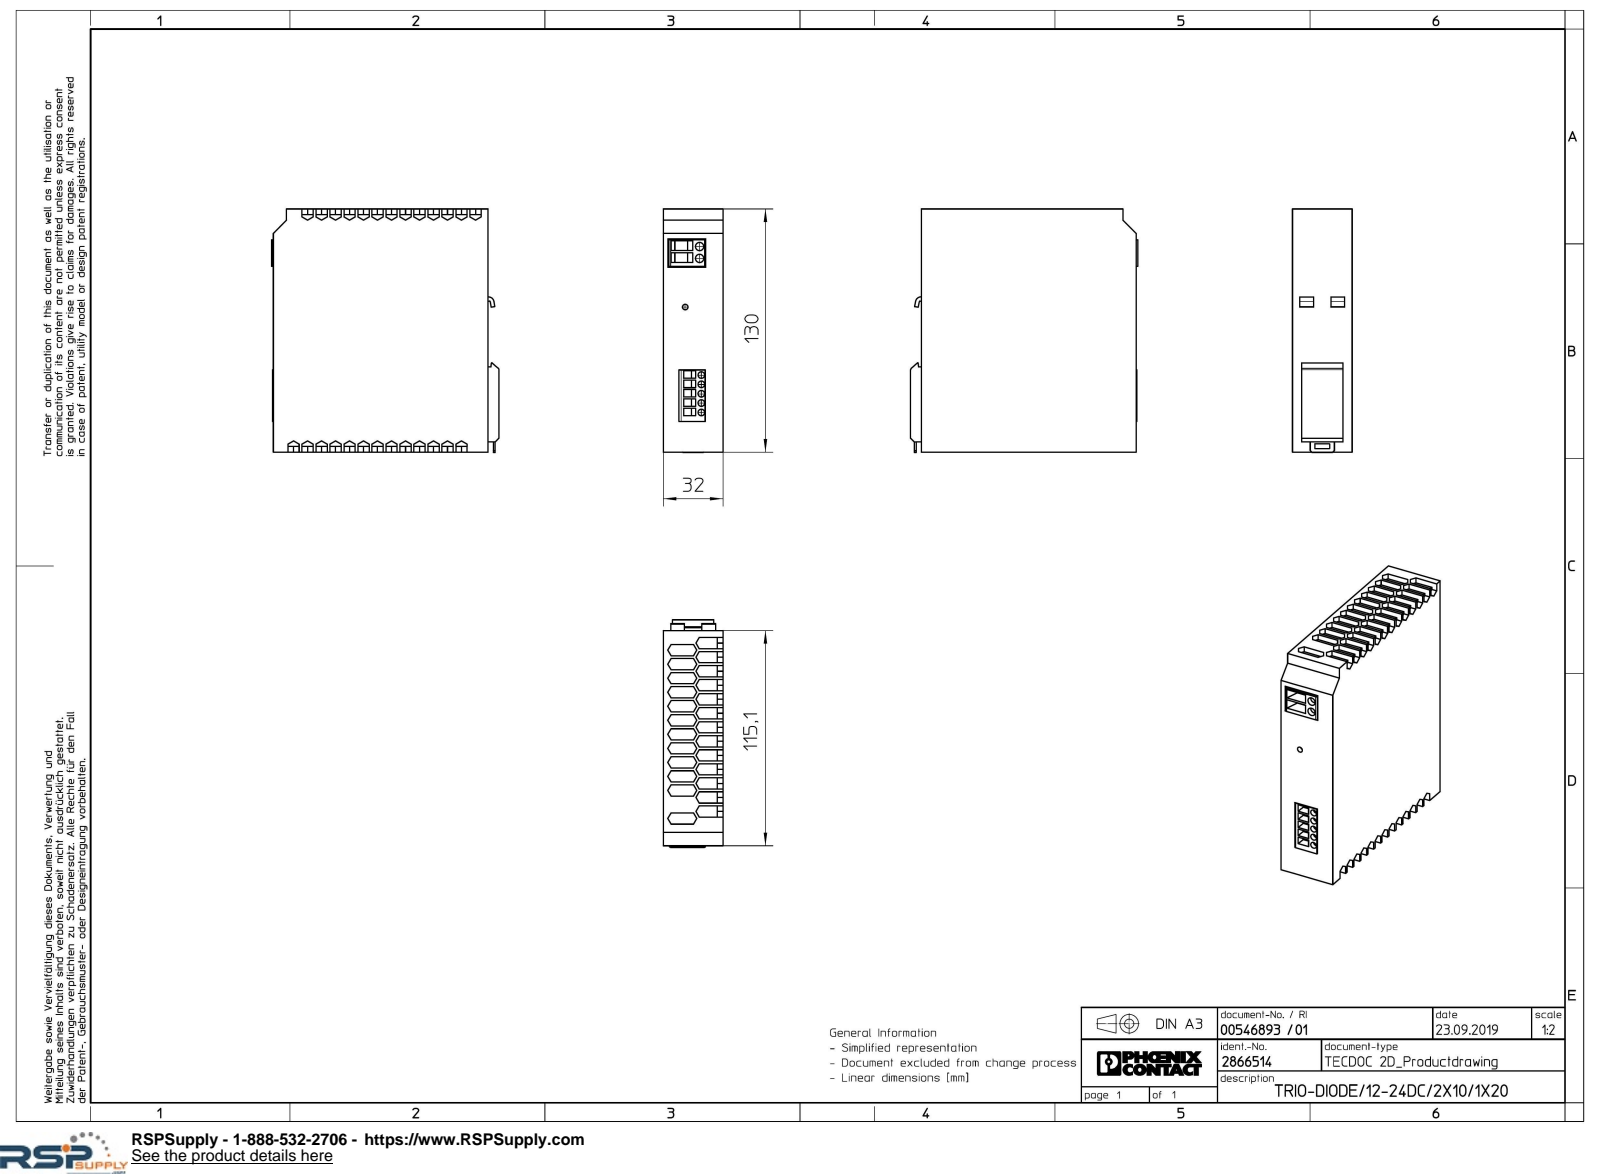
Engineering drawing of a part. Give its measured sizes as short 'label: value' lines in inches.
name: TRIO_DIODE_12_24DC_2x10_1x20-select
written by: Creo Elements/Direct Modeling 20.1A 29-Sep-2018 (C) Parametric Technology GmbH (AUTOMOTIVE_DESIGN)
unit: in
bodies: 1 solid, 519 faces (457 planar, 26 cylindrical, 36 other)
size: 5.122 × 4.794 × 1.26
volume: 28.5 in³; area: 82.05 in²
holes: 5× ⌀0.14, 2× ⌀0.177, 1× ⌀0.118
rounds: 3× R0.008, 2× R0.039, 1× R0.02, 1× R0.059, 1× R0.118
face distances: 1.26, 0.118, 5, 0.295, 4.882, 5.118, 0.591, 0.886, 0.148, 1.181
hole spacings: 0.197, 0.394, 0.591, 0.25, 0.787, 1.068, 1.309, 1.471
